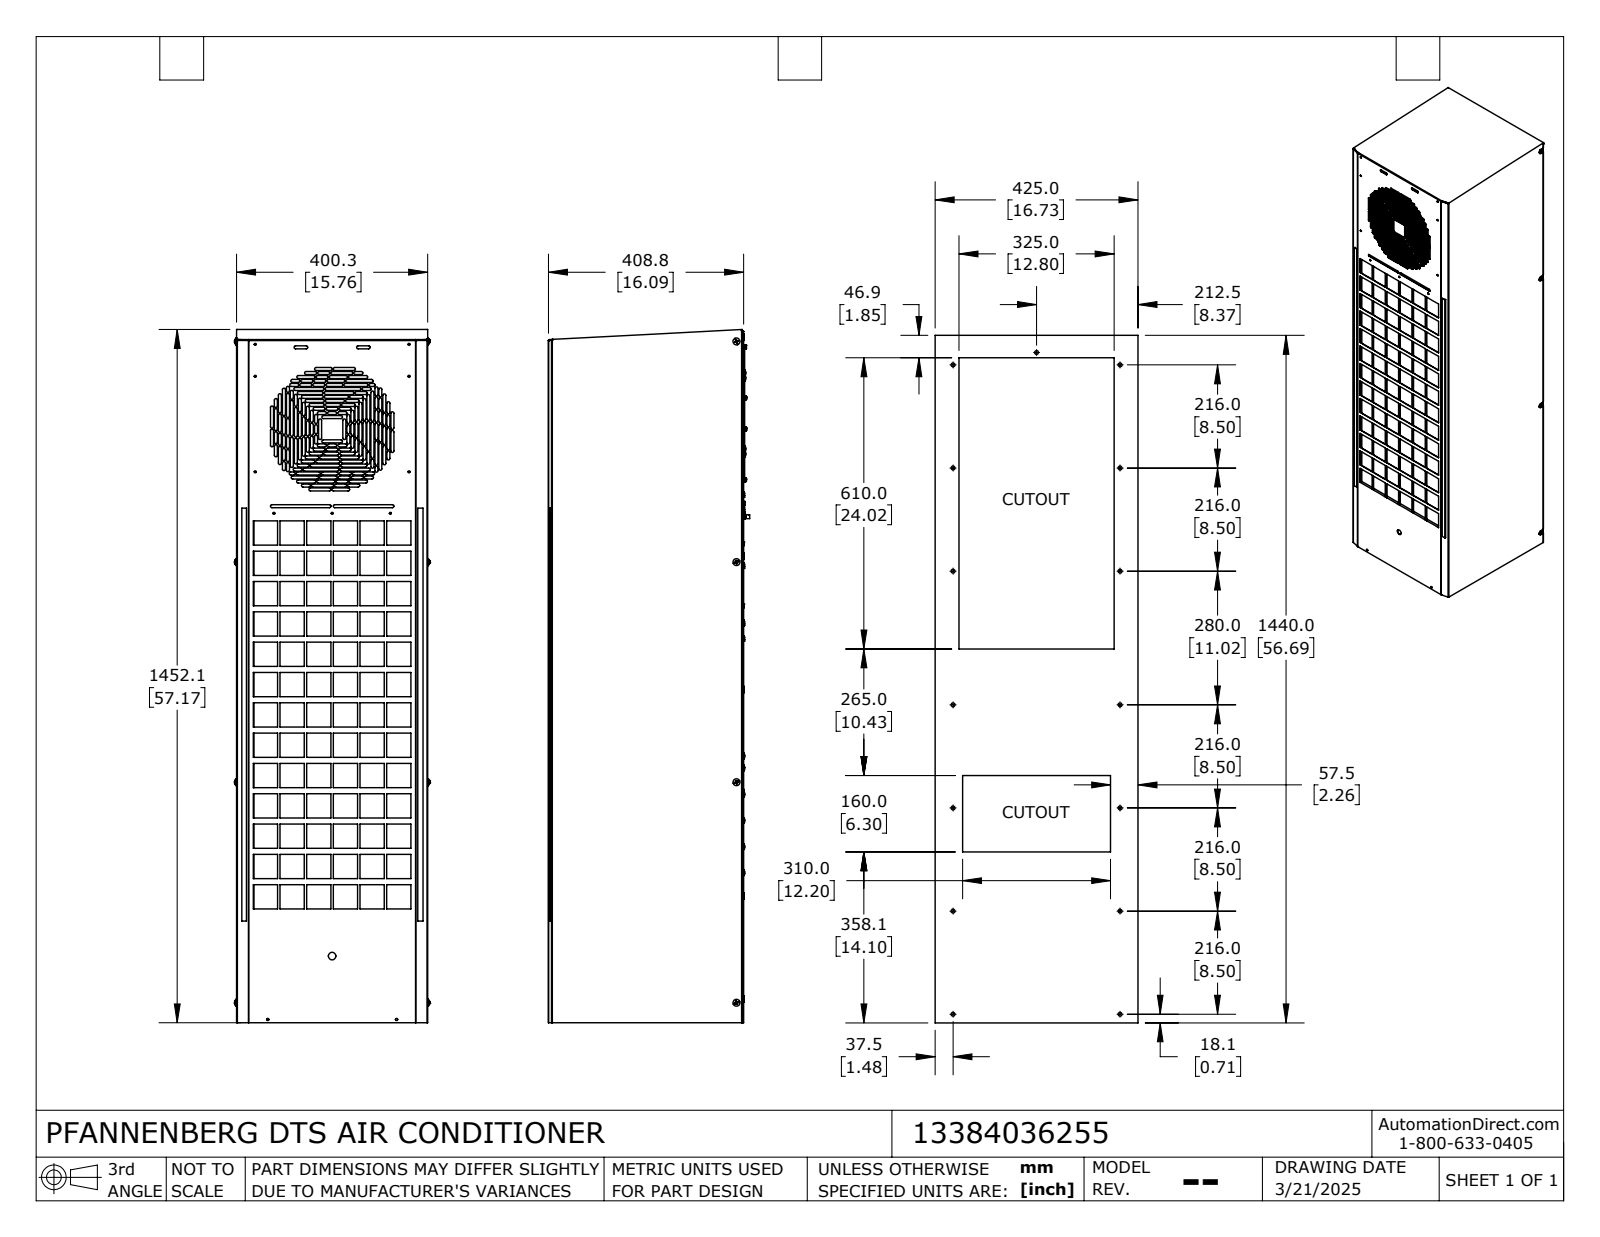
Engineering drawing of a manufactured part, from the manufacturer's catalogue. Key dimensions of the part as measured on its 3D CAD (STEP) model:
Part name (STEP PRODUCT): 13384036255_Default
STEP written by: SolidWorks 2024 (CONFIG_CONTROL_DESIGN)
Units: inches
Bodies: 1 solid, 5369 faces (3016 planar, 1488 cylindrical, 865 other)
Overall size (bounding box): 57.171 × 16.603 × 16.113
Volume: 13 807 in³ · Surface area: 6 261 in²
Round holes (diameter × count): ⌀0.107 ×35, ⌀0.165 ×27, ⌀0.283 ×15, ⌀0.189 ×14, ⌀0.098 ×4, ⌀0.161 ×4, ⌀0.125 ×2, ⌀0.276 ×2, ⌀0.945 ×2, ⌀0.122 ×1, ⌀0.625 ×1, ⌀0.731 ×1
Round bosses / shafts (diameter × count): ⌀0.178 ×22, ⌀0.512 ×15, ⌀0.315 ×12, ⌀0.157 ×12, ⌀0.122 ×12, ⌀0.354 ×6, ⌀0.079 ×5, ⌀0.573 ×4
Partial cylindrical surfaces — rounded edges, fillets, slot ends (radius × count): R0.125 ×352, R0.031 ×23, R0.198 ×15, R0.087 ×13, R0.076 ×9, R0.132 ×6, R0.118 ×5, R0.016 ×4
Main face-to-face distances: 15.759, 0.143, 0.045, 15.815, 15.672, 16.096, 15.953, 0.281, 0.236, 16.051
Hole centre spacings: 3.028, 0.022, 4.331, 1.507, 3.006, 3.05, 3.15, 4.724
